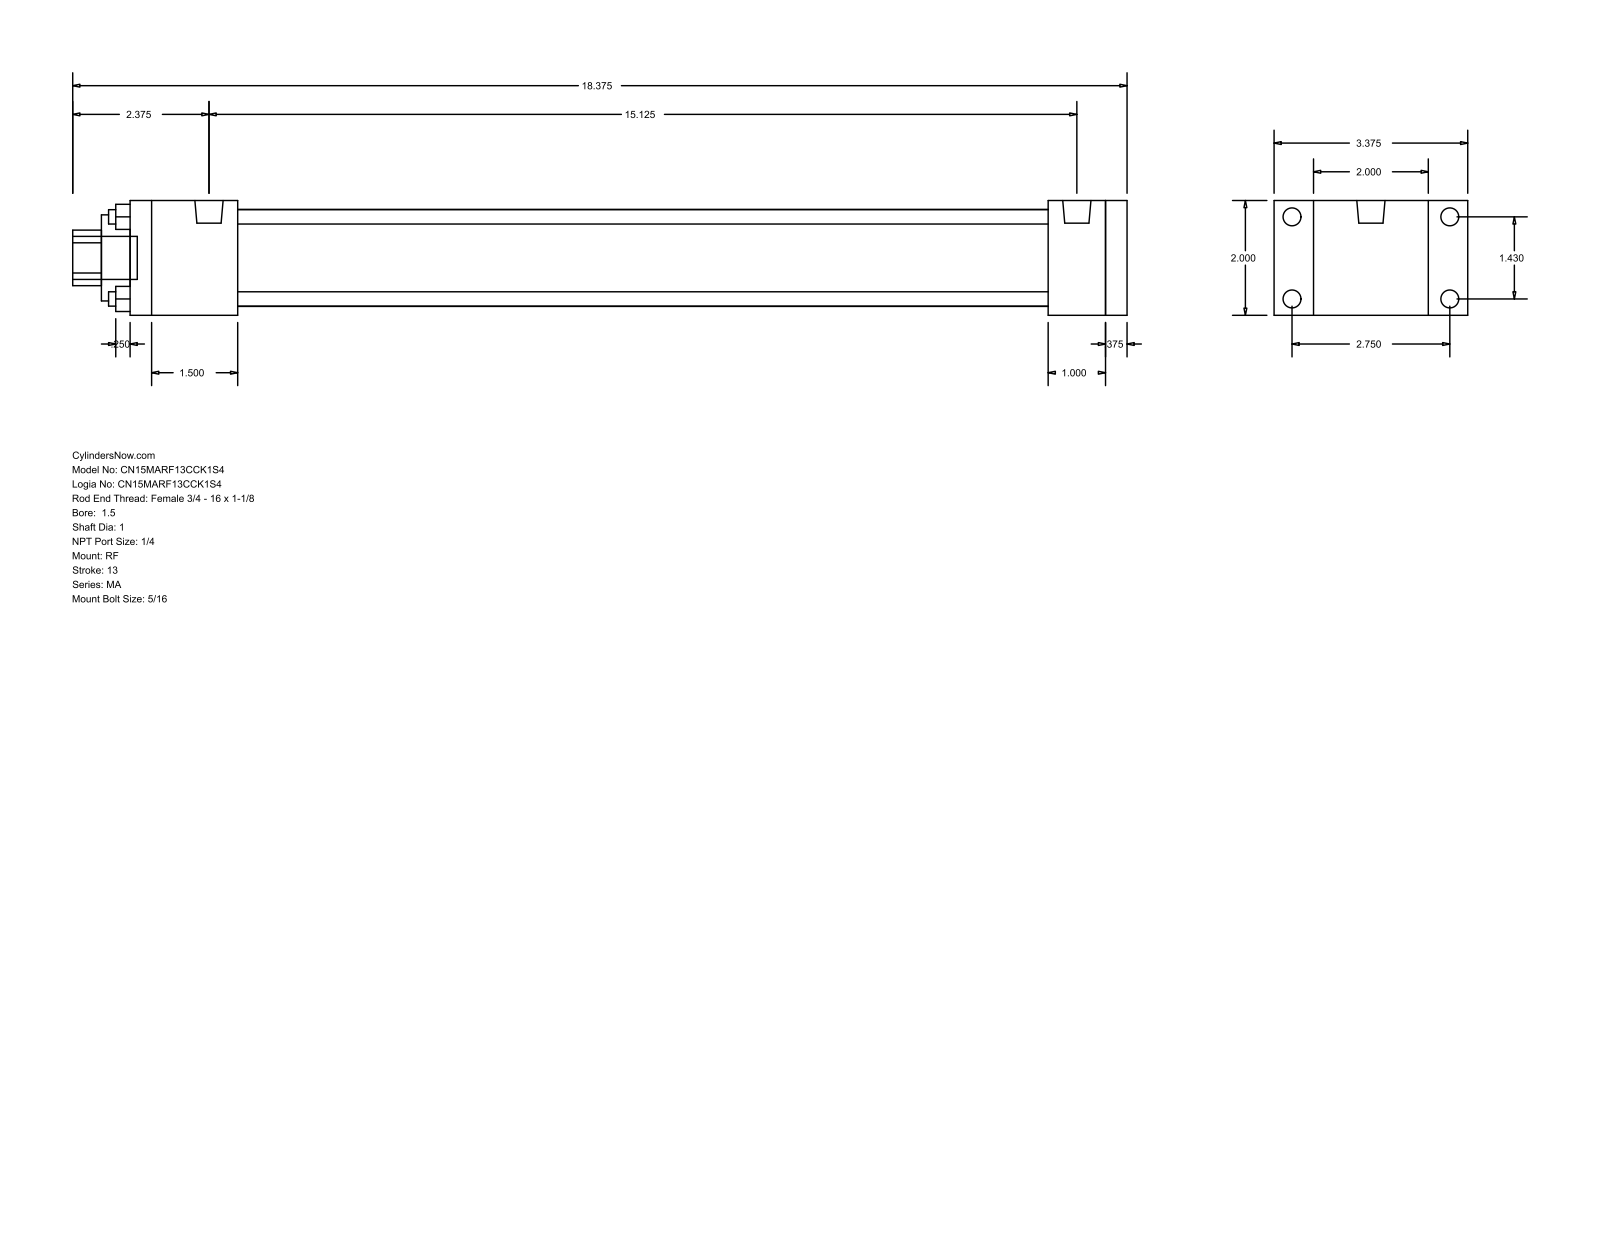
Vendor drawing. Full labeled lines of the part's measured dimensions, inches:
Part name (STEP PRODUCT): MA_RF__0150_1
STEP written by: GSSL Pune (CONFIG_CONTROL_DESIGN)
Units: inches
Bodies: 0 solids, 92 faces (64 planar, 28 cylindrical, 0 other)
Overall size (bounding box): 18.375 × 3.375 × 2
Round holes (diameter × count): ⌀0.25 ×4, ⌀1 ×1, ⌀1.5 ×1, ⌀1.69 ×1
Round bosses / shafts (diameter × count): ⌀0.313 ×8, ⌀0.492 ×2, ⌀0.75 ×1
Partial cylindrical surfaces — rounded edges, fillets, slot ends (radius × count): R0.484 ×1
Main face-to-face distances: 2, 0.375, 17, 1, 17.375, 16, 1.375, 1.875, 14.125, 15.125
Hole centre spacings: 1.011, 1.43, 2.022
